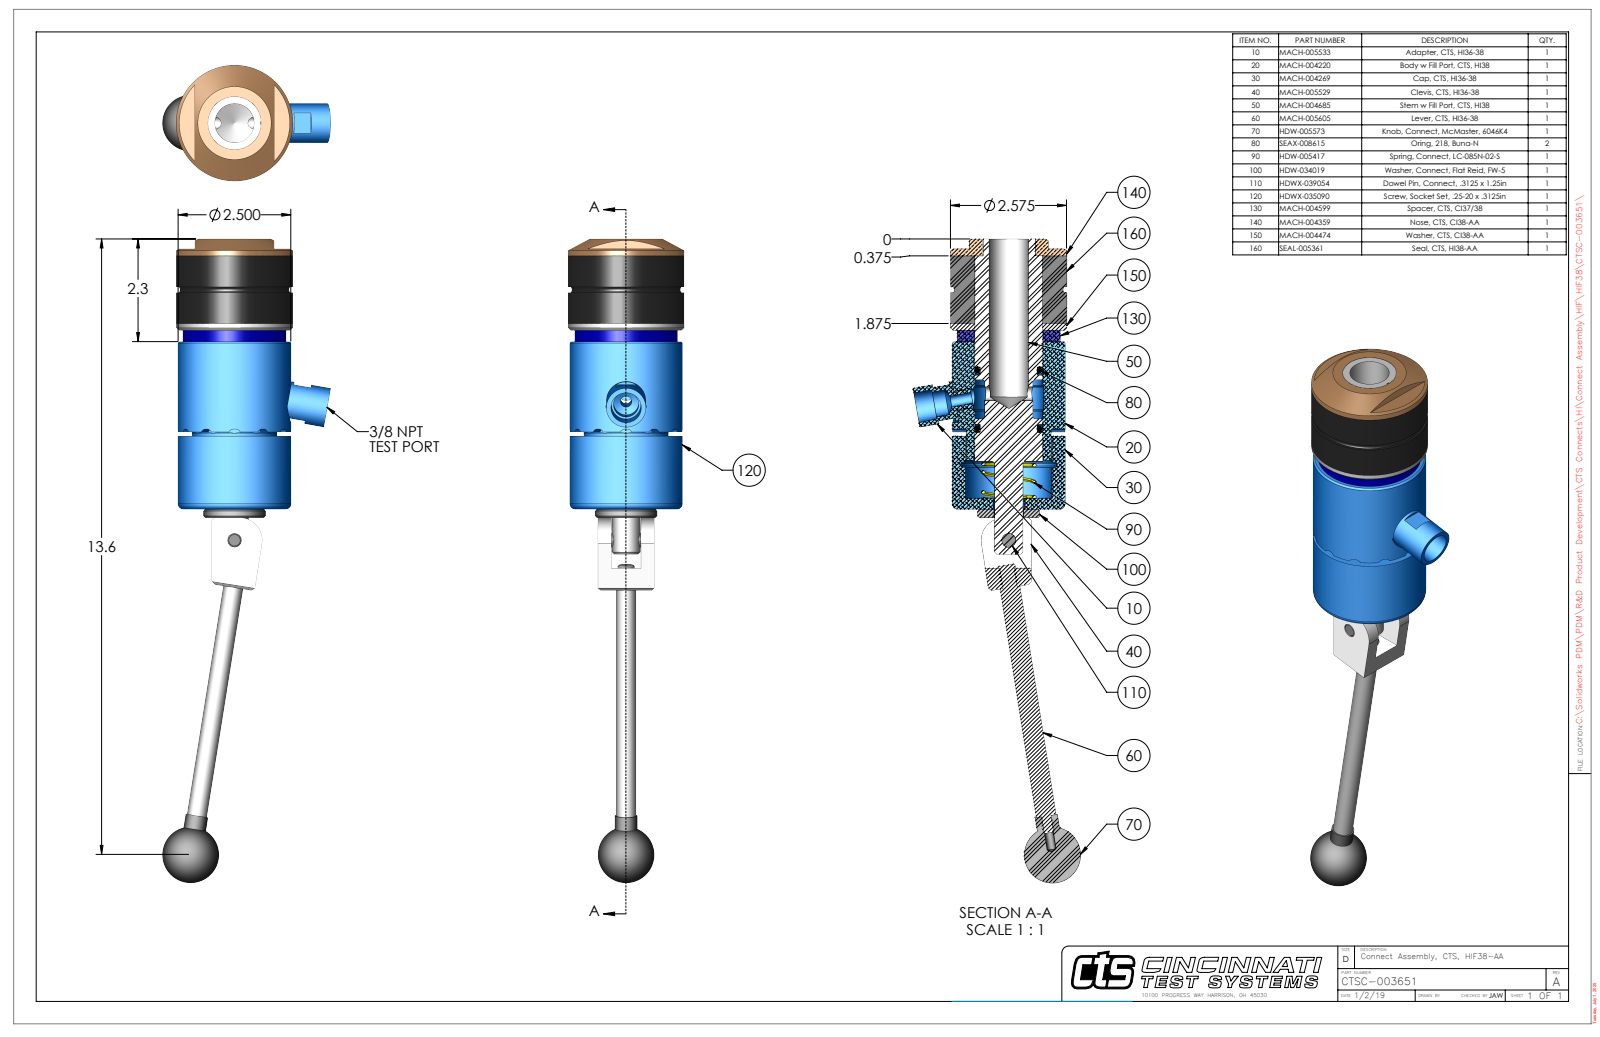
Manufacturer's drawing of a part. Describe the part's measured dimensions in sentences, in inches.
The part is named "CTSC-003651". Its 3-D file was written by "SolidWorks 2023 (AUTOMOTIVE_DESIGN)". It is 10 solids with 369 faces: 158 planar, 126 cylindrical and 85 other. Overall it measures 14.275 by 3.716 by 2.575 inches. Its volume is 30.66 cubic inches and its surface area 154.3 square inches. Round holes: 2 of diameter 0.201, 1 of diameter 0.15, 1 of diameter 0.25, 1 of diameter 0.311, 1 of diameter 0.312, 1 of diameter 0.313, 1 of diameter 0.314, 1 of diameter 0.562, 1 of diameter 0.656, 1 of diameter 0.696, 1 of diameter 0.875, 1 of diameter 1.172. Round bosses or shafts: 1 of diameter 2.575, 1 of diameter 2.575, 1 of diameter 2.5, 1 of diameter 2.281, 1 of diameter 1.875, 1 of diameter 1.5, 1 of diameter 1.498, 1 of diameter 1.38. Partial cylindrical surfaces (rounded edges, fillets, slot ends): 12 of radius 0.12, 2 of radius 0.029, 1 of radius 0.19, 1 of radius 0.195, 1 of radius 0.47, 1 of radius 0.476, 1 of radius 0.5, 1 of radius 1.193. The main face-to-face distances are 1.5, 0.152, 1.652, 0.25, 0.402, 1.902, 3.713, 3.963, 4.115, 5.615. The hole center spacings are 0.74, 2.118, 2.858.
